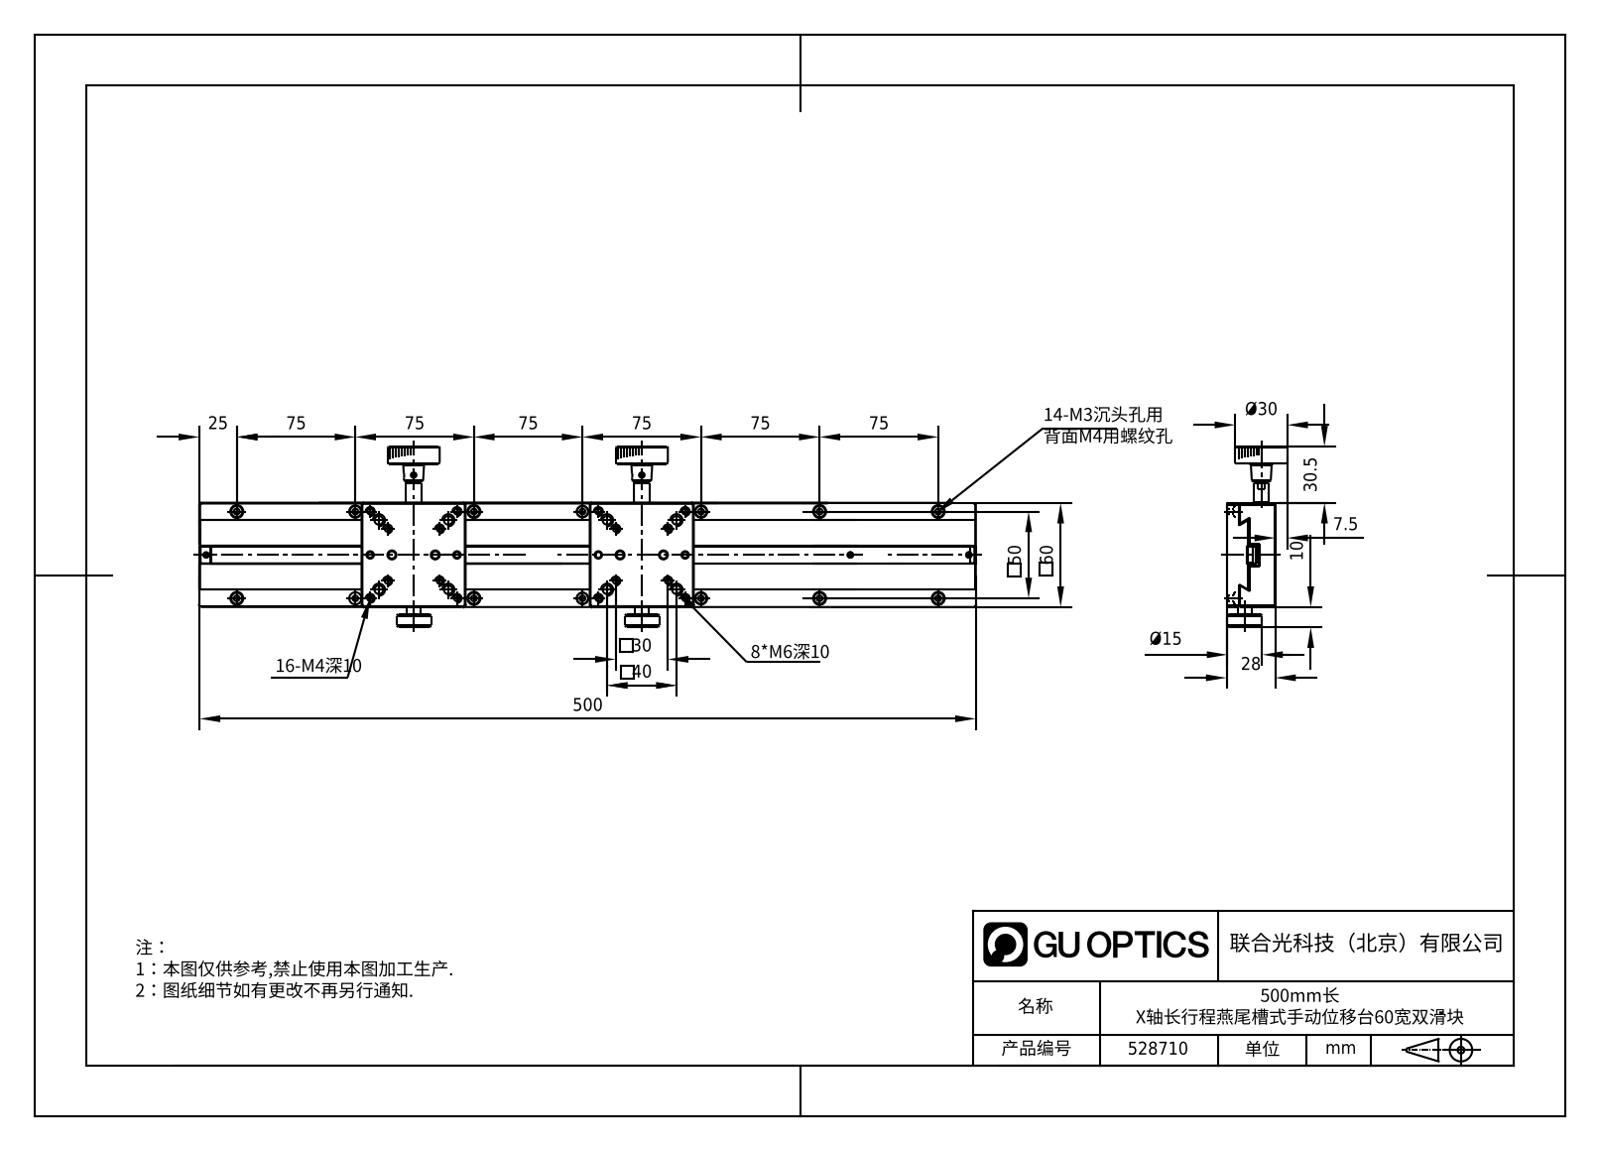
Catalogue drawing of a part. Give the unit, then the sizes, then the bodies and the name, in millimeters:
Units: millimetres
Overall size (bounding box): 500 × 101.79 × 33.1
Round holes (diameter × count): ⌀3.3 ×36, ⌀2.5 ×20, ⌀5 ×15, ⌀6 ×14, ⌀2.05 ×7, ⌀2.9 ×7, ⌀4 ×2, ⌀4.1 ×2, ⌀4.5 ×2, ⌀8 ×2, ⌀10 ×2
Round bosses / shafts (diameter × count): ⌀3 ×10, ⌀4.5 ×5, ⌀2.5 ×5, ⌀9 ×4, ⌀4 ×4, ⌀30 ×2, ⌀10 ×2, ⌀8 ×2
Main face-to-face distances: 7.5, 4.7, 12.2, 9.9, 2.4, 2.3, 60, 28, 20.5, 18.1
Hole centre spacings: 79.06, 75, 25, 152.07, 7.07, 35.36, 41.23, 45.28
Volume: 441 488 mm³ · Surface area: 141 188 mm²
Bodies: 33 solids, 1216 faces (544 planar, 285 cylindrical, 387 other)
Part name (STEP PRODUCT): 5287101
STEP written by: SolidWorks 2020 (CONFIG_CONTROL_DESIGN)
